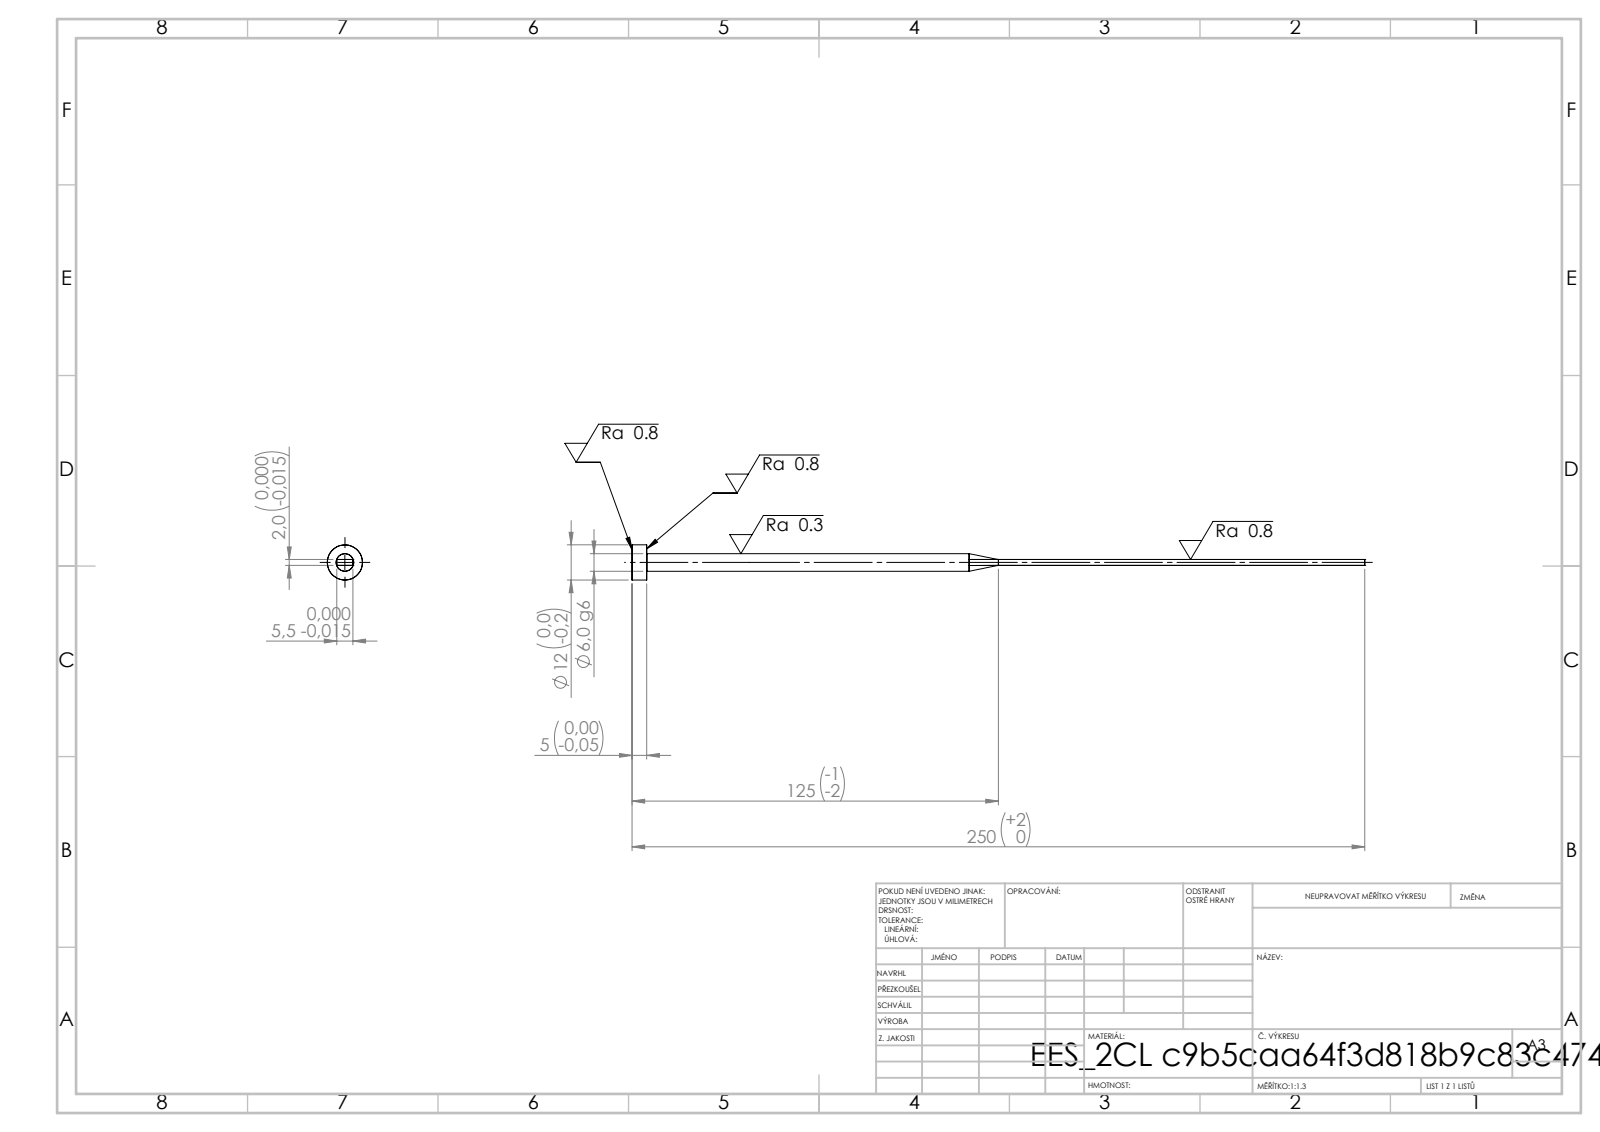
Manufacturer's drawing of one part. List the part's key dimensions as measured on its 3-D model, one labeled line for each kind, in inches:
STEP written by: SolidWorks 2019 (CONFIG_CONTROL_DESIGN)
Units: inches
Bodies: 1 solid, 15 faces (7 planar, 4 cylindrical, 4 other)
Overall size (bounding box): 9.843 × 0.472 × 0.472
Volume: 0.32 in³ · Surface area: 6.992 in²
Round bosses / shafts (diameter × count): ⌀0.472 ×1, ⌀0.236 ×1
Main face-to-face distances: 0.079, 0.217, 0.197, 9.843, 9.646
